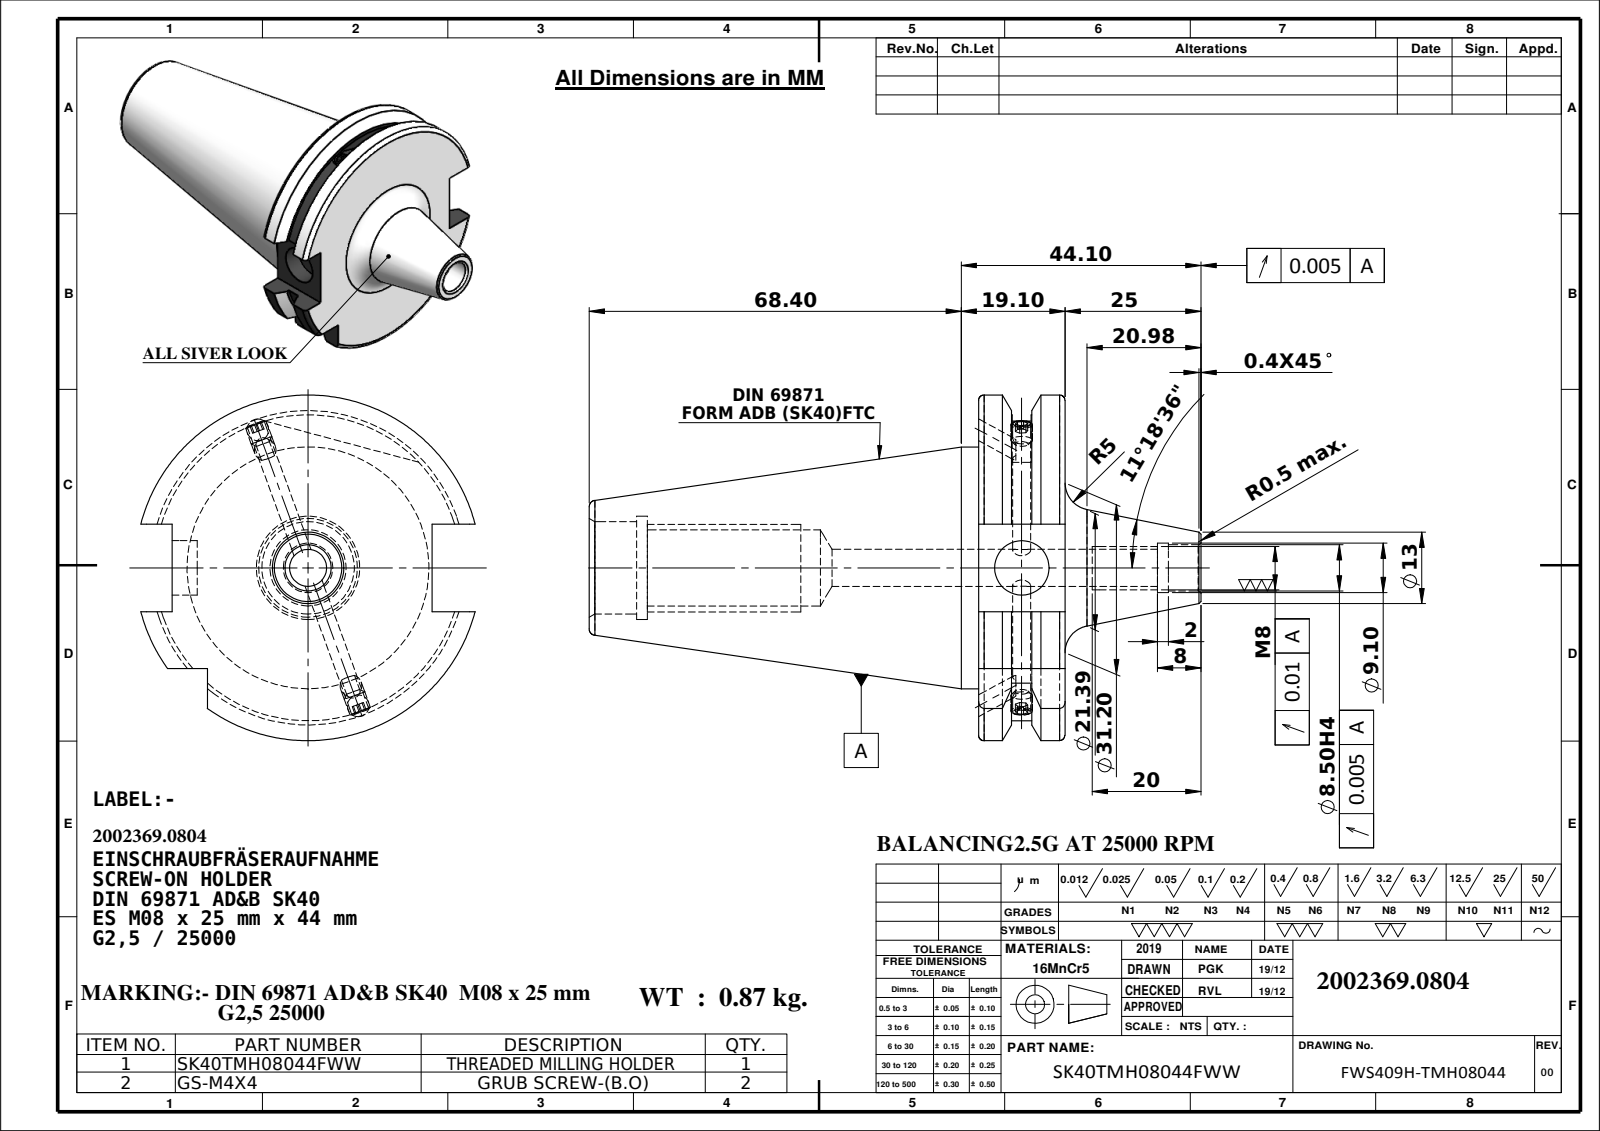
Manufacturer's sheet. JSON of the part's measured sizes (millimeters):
{"part_name": "91406-ES7M08025", "step_written_by": "SolidWorks 2018 (AUTOMOTIVE_DESIGN)", "units": "millimeters", "bodies": {"solids": 1, "faces": 98, "planar": 30, "cylindrical": 32, "other": 36}, "overall_size": [112.5, 63.55, 61.48], "volume_mm3": 109109, "surface_area_mm2": 22186, "round_holes": [[3.3, 1], [6.8, 1], [8.5, 1], [9.1, 1], [10, 1], [14, 1], [17, 1], [19, 1]], "round_bosses_or_shafts": [[44.45, 1]], "partial_cylinders_radius": [[28.12, 1], [31.77, 1]], "face_to_face_distances": [15.9, 16.1, 47.8, 71.6, 87.5, 10.7, 60.9, 76.8, 77.62, 66.92]}
